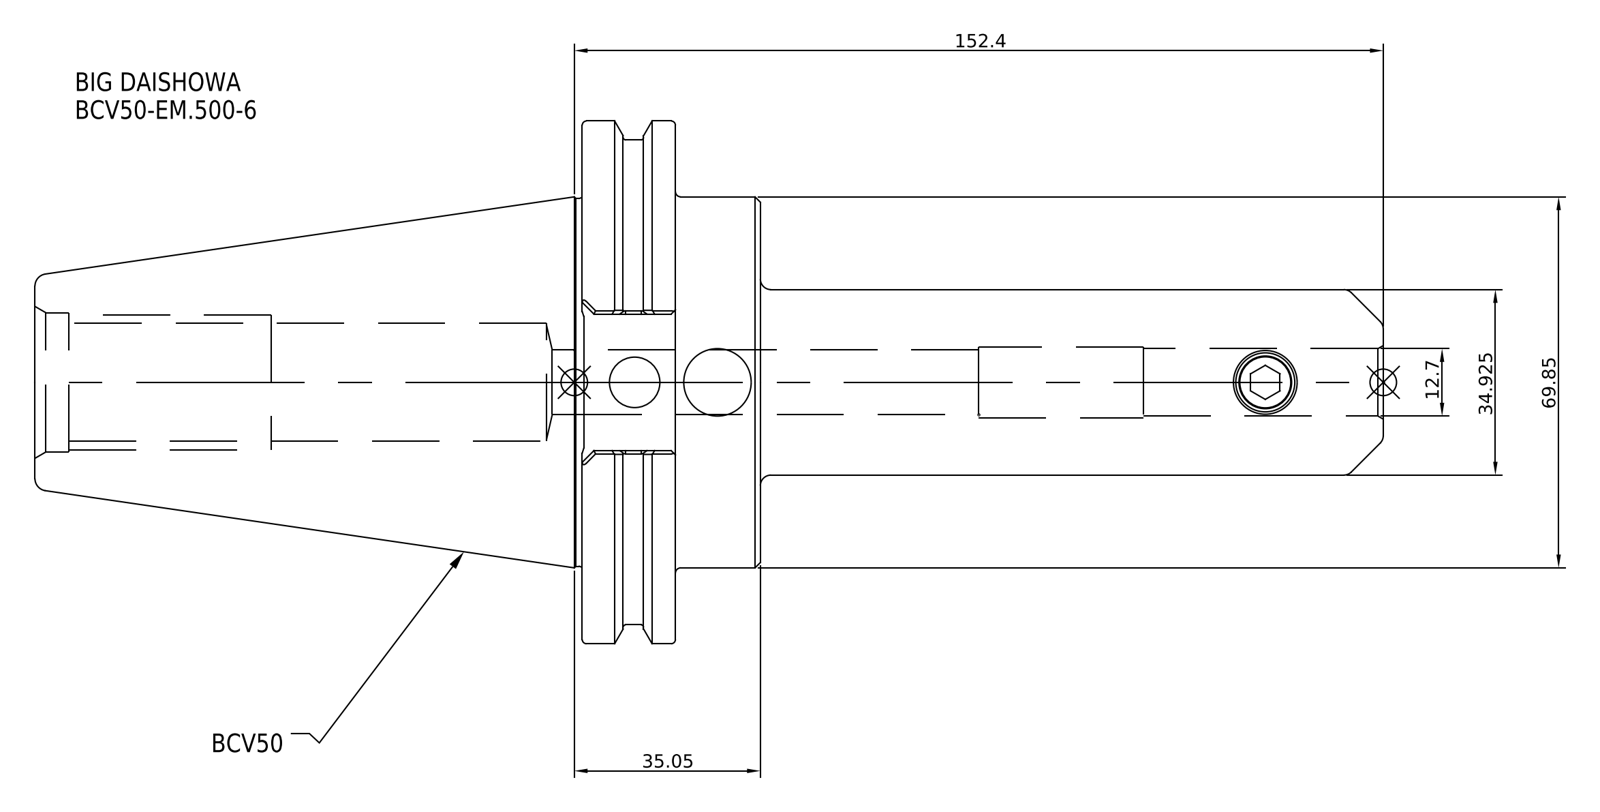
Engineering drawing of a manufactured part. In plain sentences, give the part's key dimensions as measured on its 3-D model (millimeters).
The part is named "BCV50-EM_500-6". Its 3-D file was written by "SolidWorks 2021 (CONFIG_CONTROL_DESIGN)". It is 1 solid with 30 faces: 8 planar, 14 cylindrical and 8 other. Overall it measures 254 by 98.43 by 98.43 millimeters. Its volume is 538 170 cubic millimeters and its surface area 58 063 square millimeters. Round holes: 1 of diameter 12.7. Round bosses or shafts: 1 of diameter 98.43, 1 of diameter 91.29, 1 of diameter 69.85, 1 of diameter 34.93. The main face-to-face distances are 17.55, 16, 33.55, 136.65, 120.65, 103.1, 117.35, 133.35, 150.9, 254.
